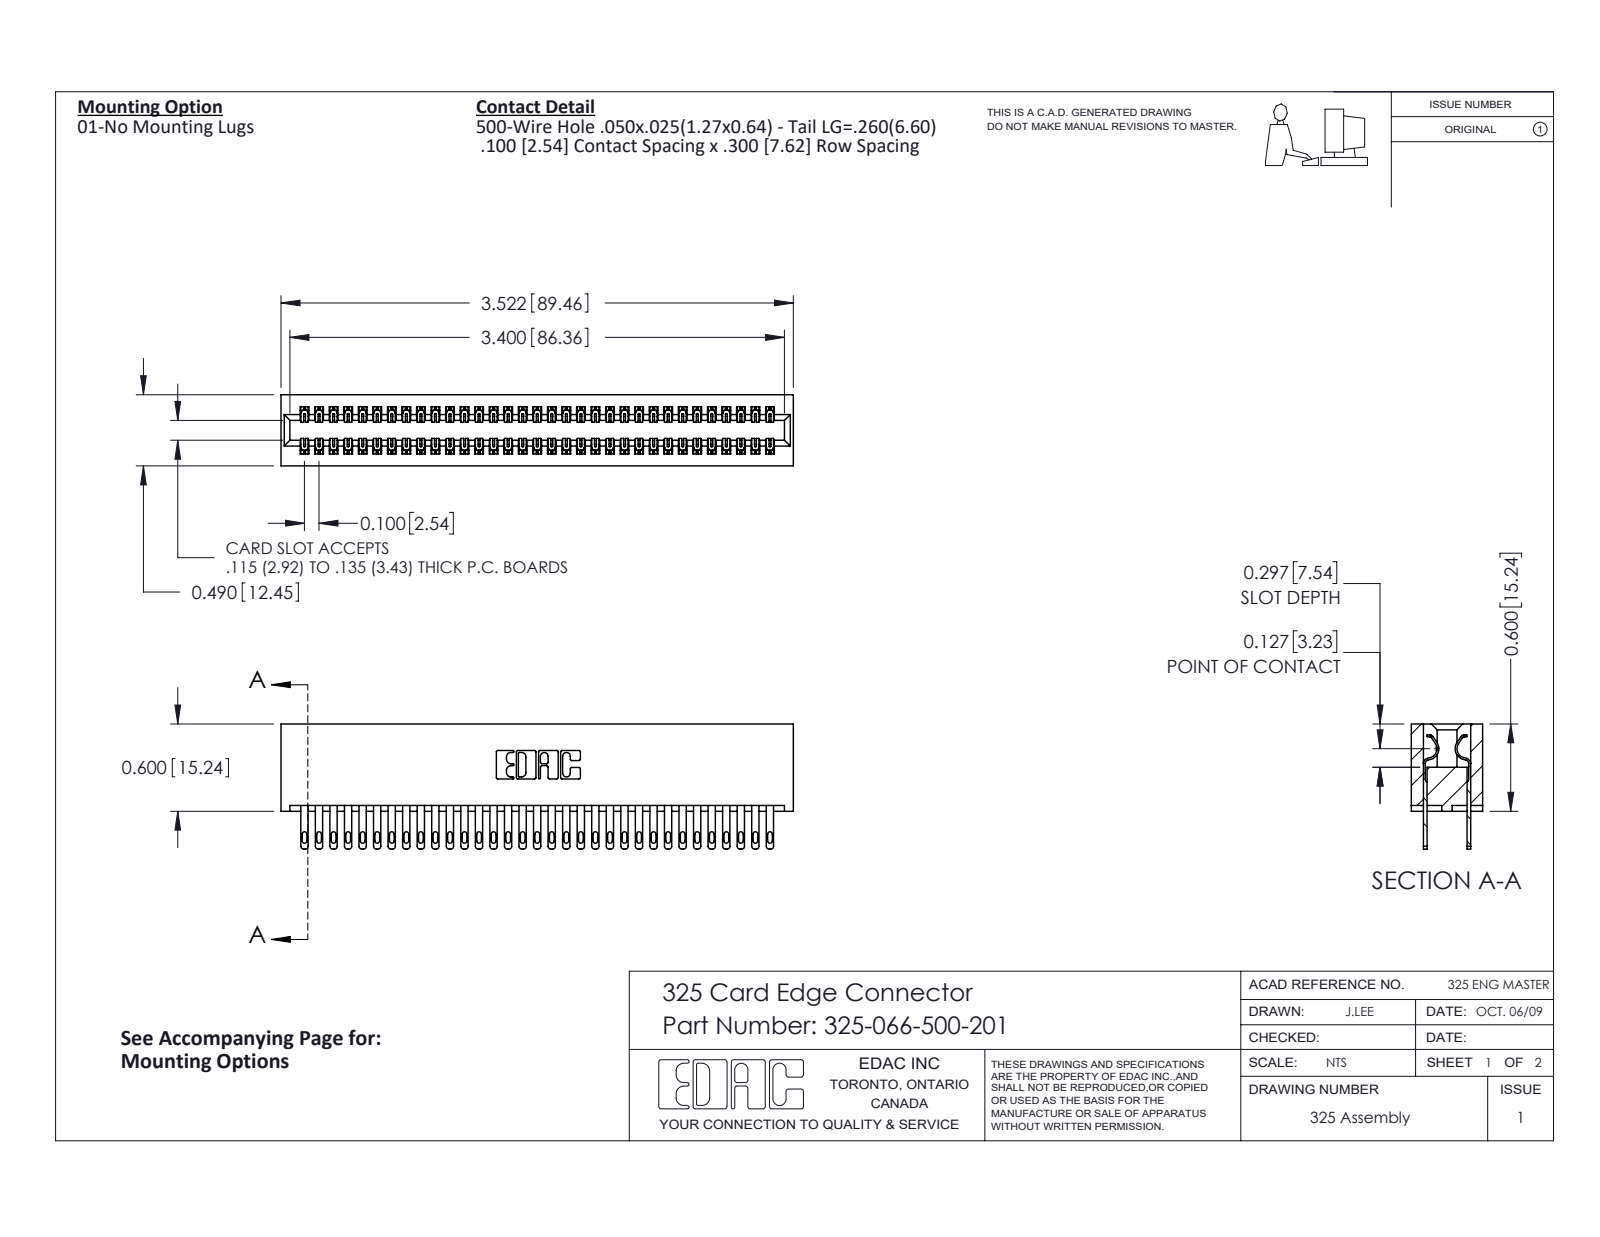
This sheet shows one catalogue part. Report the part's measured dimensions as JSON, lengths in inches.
{"part_name": "325-066-500-201; 325 Part_Lugless; 325-292-001_325-293-100", "step_written_by": "SolidWorks 2016 (CONFIG_CONTROL_DESIGN)", "units": "inches", "bodies": {"solids": 67, "faces": 3274, "planar": 2046, "cylindrical": 1228, "other": 0}, "overall_size": [3.522, 0.86, 0.49], "volume_in3": 0.749, "surface_area_in2": 24.79, "partial_cylinders_radius": [[0.006, 99], [0.016, 66], [0.02, 66], [0.01, 22], [0.007, 6], [0.031, 6], [0.026, 3], [0.014, 2]], "face_to_face_distances": [0.083, 0.407, 0.3, 0.107, 0.383, 0.025, 0.325, 0.49, 0.275, 0.56]}
